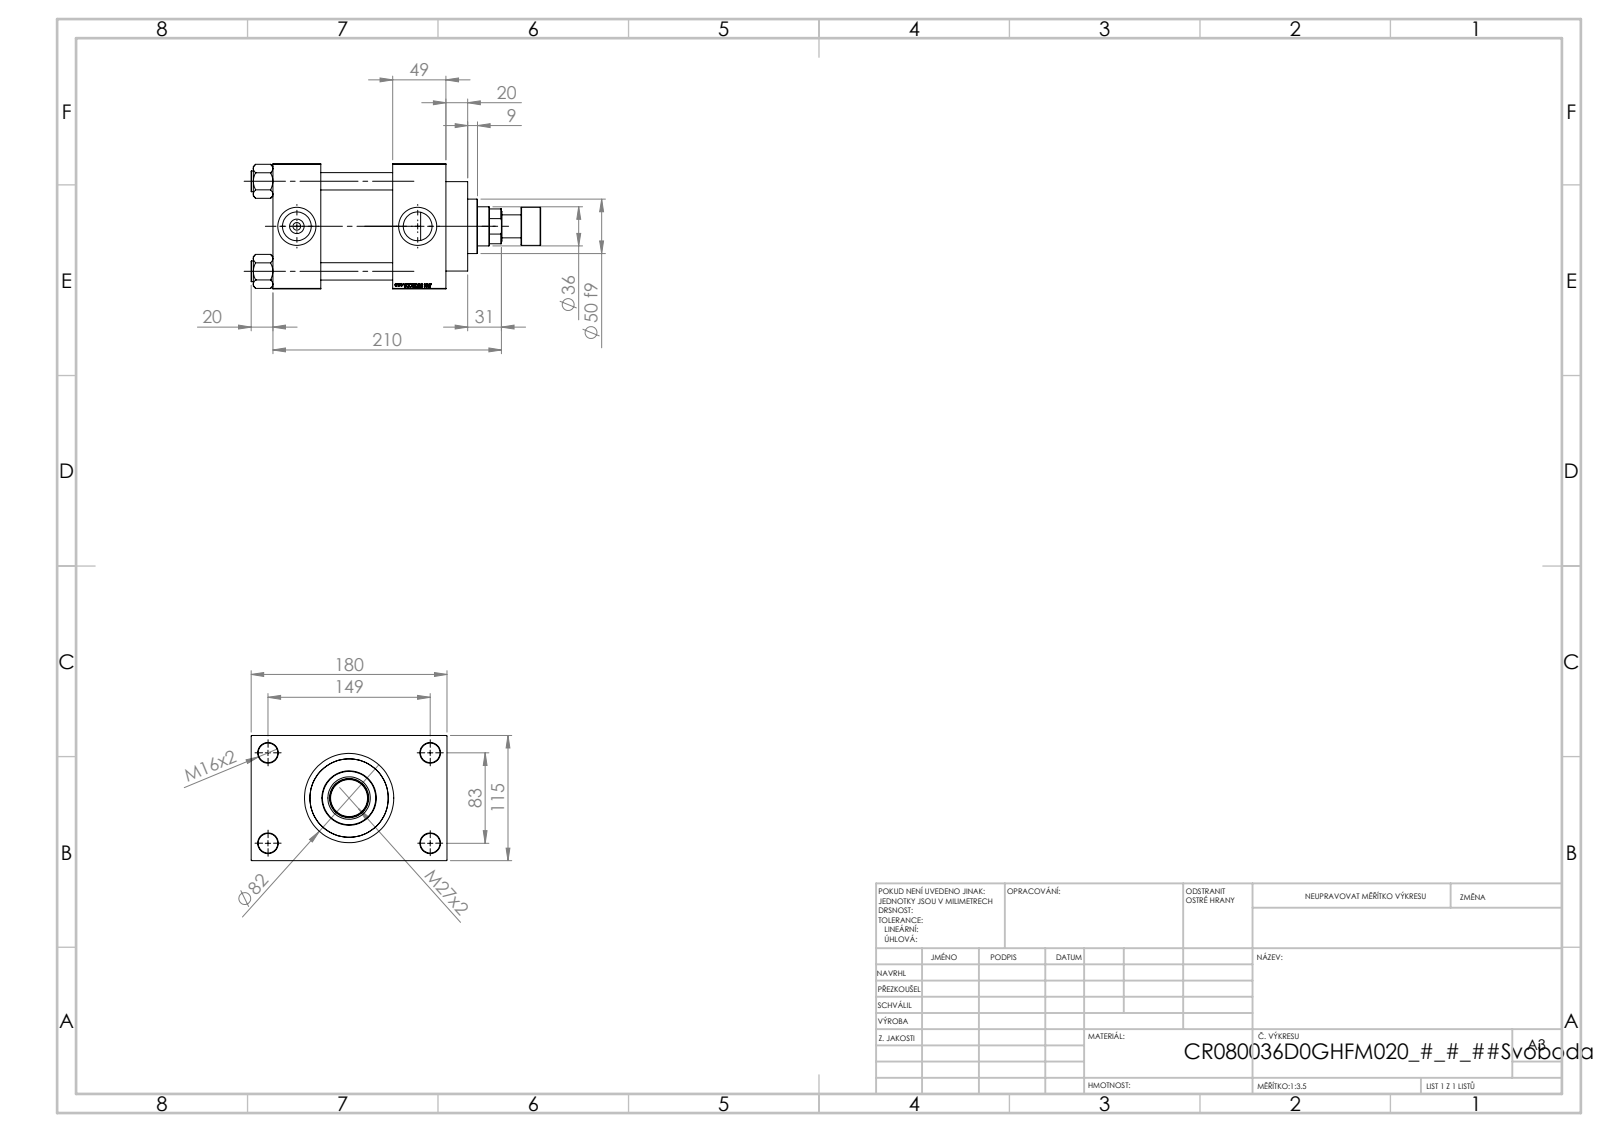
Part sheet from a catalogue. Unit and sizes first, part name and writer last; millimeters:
Units: millimetres
Overall size (bounding box): 266 × 180 × 115
Round holes (diameter × count): ⌀16 ×4, ⌀18 ×4, ⌀7 ×2, ⌀26.44 ×2, ⌀35 ×2, ⌀25.5 ×1, ⌀36 ×1, ⌀39 ×1, ⌀61 ×1, ⌀72 ×1, ⌀80 ×1
Round bosses / shafts (diameter × count): ⌀19 ×4, ⌀86 ×1, ⌀82 ×1, ⌀50 ×1, ⌀35 ×1, ⌀21 ×1
Main face-to-face distances: 115, 66, 49, 110, 44, 159, 32.5, 147.5, 20, 69
Hole centre spacings: 33.15, 58.48, 82.7, 85.28, 89.24, 115.85, 142.43, 83
Volume: 2 003 000 mm³ · Surface area: 302 161 mm²
Bodies: 12 solids, 1165 faces (549 planar, 92 cylindrical, 524 other)
Part name (STEP PRODUCT): V215CR_D_Body; NUT_M5_D; V215CR_D_TYCINKA; V215_VC_A (+2 more)
STEP written by: SolidWorks 2019 (CONFIG_CONTROL_DESIGN)
